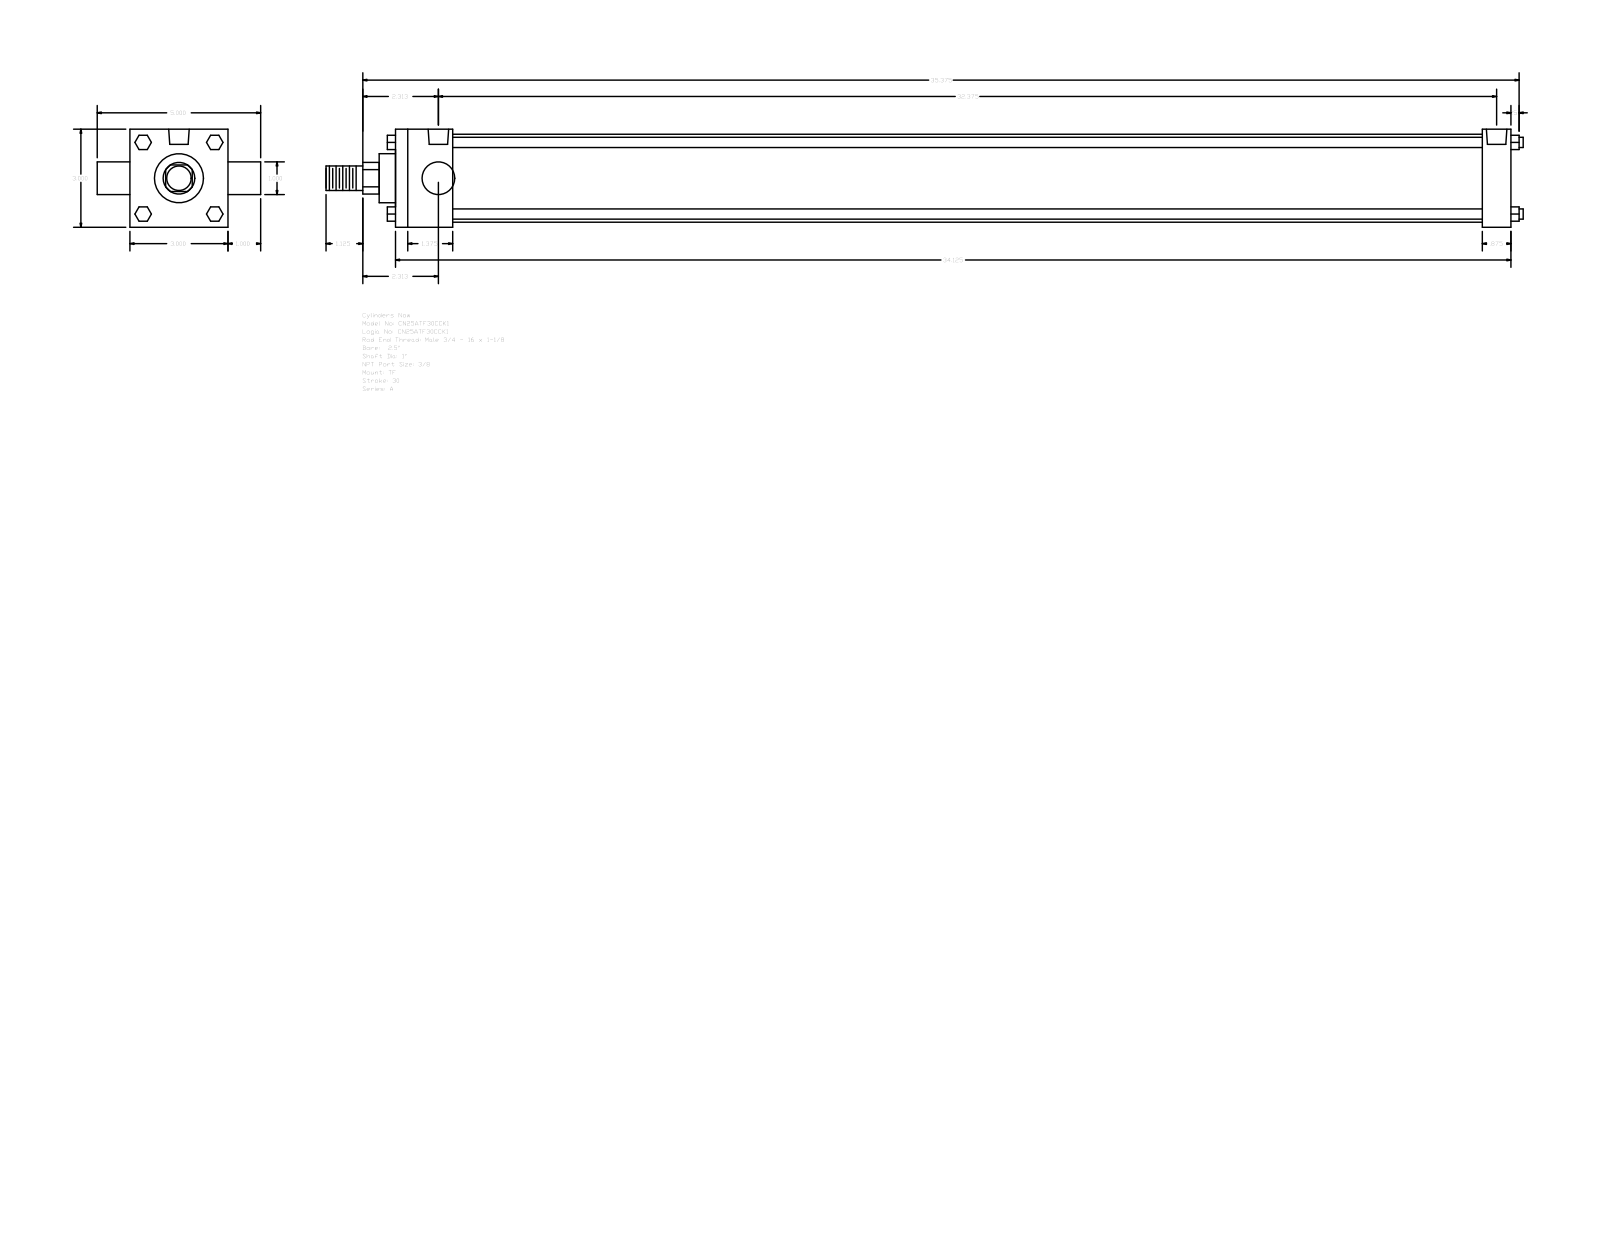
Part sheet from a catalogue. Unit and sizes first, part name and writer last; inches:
Units: inches
Overall size (bounding box): 36.625 × 5 × 3
Round holes (diameter × count): ⌀0.219 ×3, ⌀0.627 ×2
Round bosses / shafts (diameter × count): ⌀0.313 ×4, ⌀1 ×2, ⌀2.69 ×1, ⌀1.5 ×1, ⌀0.75 ×1
Partial cylindrical surfaces — rounded edges, fillets, slot ends (radius × count): R0.484 ×1
Main face-to-face distances: 3, 34.125, 1.75, 33.25, 31.5, 32.375, 0.875, 1, 4, 34.625
Hole centre spacings: 0.094, 32.469, 32.375, 32.562
Bodies: 0 solids, 120 faces (92 planar, 28 cylindrical, 0 other)
Part name (STEP PRODUCT): A_TF__0250_1
STEP written by: GSSL Pune (CONFIG_CONTROL_DESIGN)
